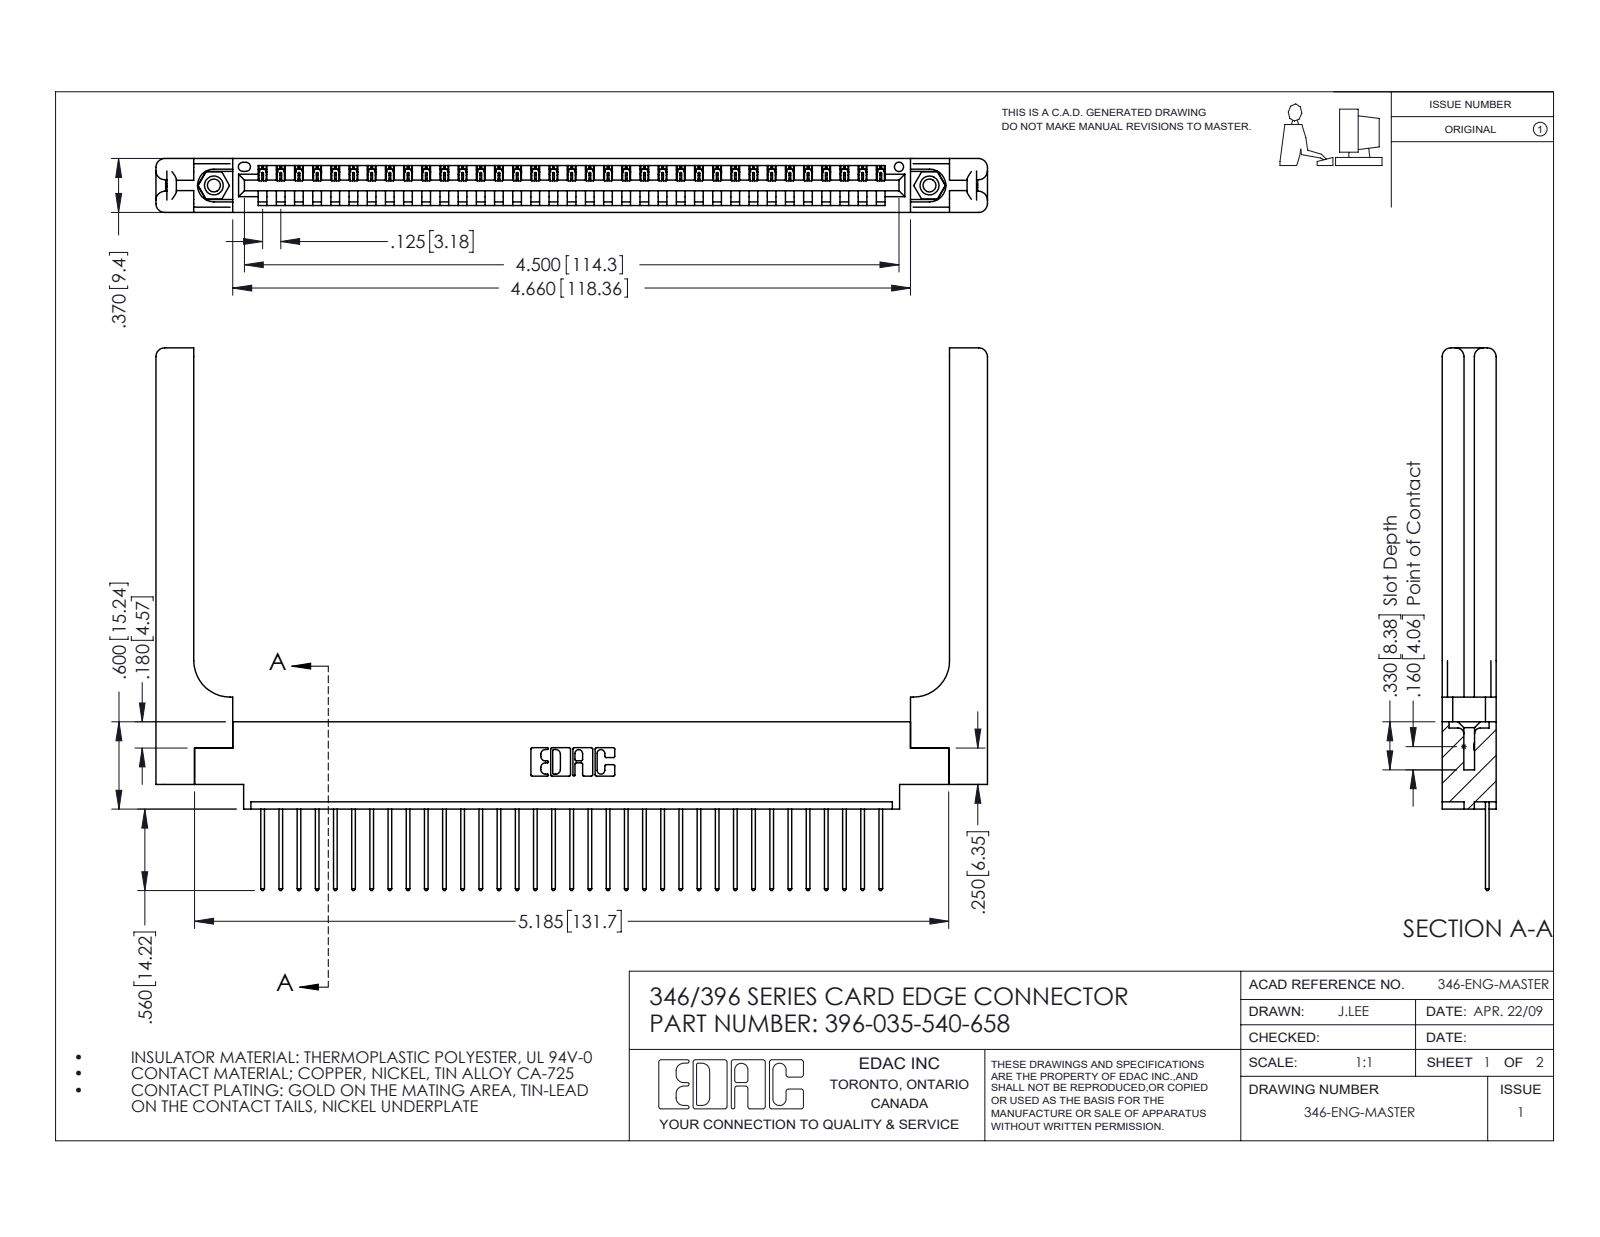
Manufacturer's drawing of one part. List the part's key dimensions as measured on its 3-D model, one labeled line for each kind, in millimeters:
Part name (STEP PRODUCT): 396-035-540-658; 345-292-001_345-293-140; 346-220-058_345-220-058; 345-250-001_345-250-001-102 (+1 more)
STEP written by: SolidWorks 2016 (CONFIG_CONTROL_DESIGN)
Units: millimetres
Bodies: 40 solids, 2412 faces (1628 planar, 724 cylindrical, 60 other)
Overall size (bounding box): 145.2 × 94.7 × 9.4
Volume: 21 250 mm³ · Surface area: 22 770 mm²
Round holes (diameter × count): ⌀2.3 ×2, ⌀3.2 ×2, ⌀4 ×2, ⌀1.6 ×1
Round bosses / shafts (diameter × count): ⌀3.9 ×2
Partial cylindrical surfaces — rounded edges, fillets, slot ends (radius × count): R0.2 ×70, R0.3 ×70, R0.3 ×22, R1.5 ×16, R0.2 ×6, R0.8 ×6, R0.7 ×3, R0.8 ×2
Main face-to-face distances: 9.4, 1.2, 8.2, 1.8, 3.8, 3.8, 6.4, 7.6, 0.6, 5.6
Hole centre spacings: 6.2, 119.7, 125
